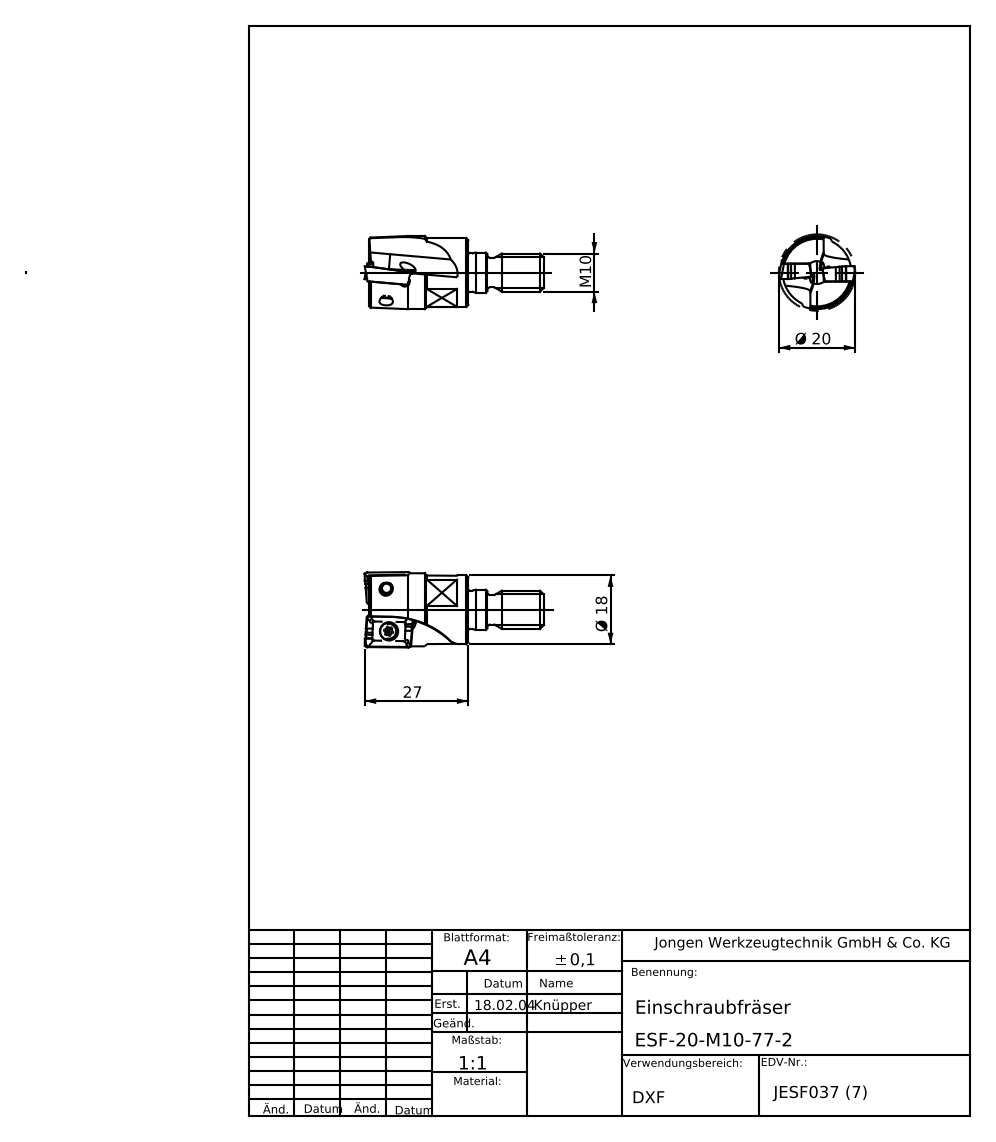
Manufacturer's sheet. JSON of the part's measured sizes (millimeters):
{"part_name": "ESF-20-M10-77-2", "step_written_by": "SolidWorks 2012 (AUTOMOTIVE_DESIGN)", "units": "millimeters", "bodies": {"solids": 1, "faces": 95, "planar": 30, "cylindrical": 29, "other": 36}, "overall_size": [46.8, 20, 20], "volume_mm3": 8125, "surface_area_mm2": 3503, "round_holes": [[2.1, 2], [3.3, 1]], "round_bosses_or_shafts": [[18, 1], [10.5, 1], [10.1, 1], [10, 1], [7.7, 1]], "partial_cylinders_radius": [[2, 4], [1.25, 2], [23.96, 2], [9.58, 1]], "face_to_face_distances": [16, 19.8, 8, 11, 30.8, 13.9, 24.9, 44.7, 21.9, 3]}
